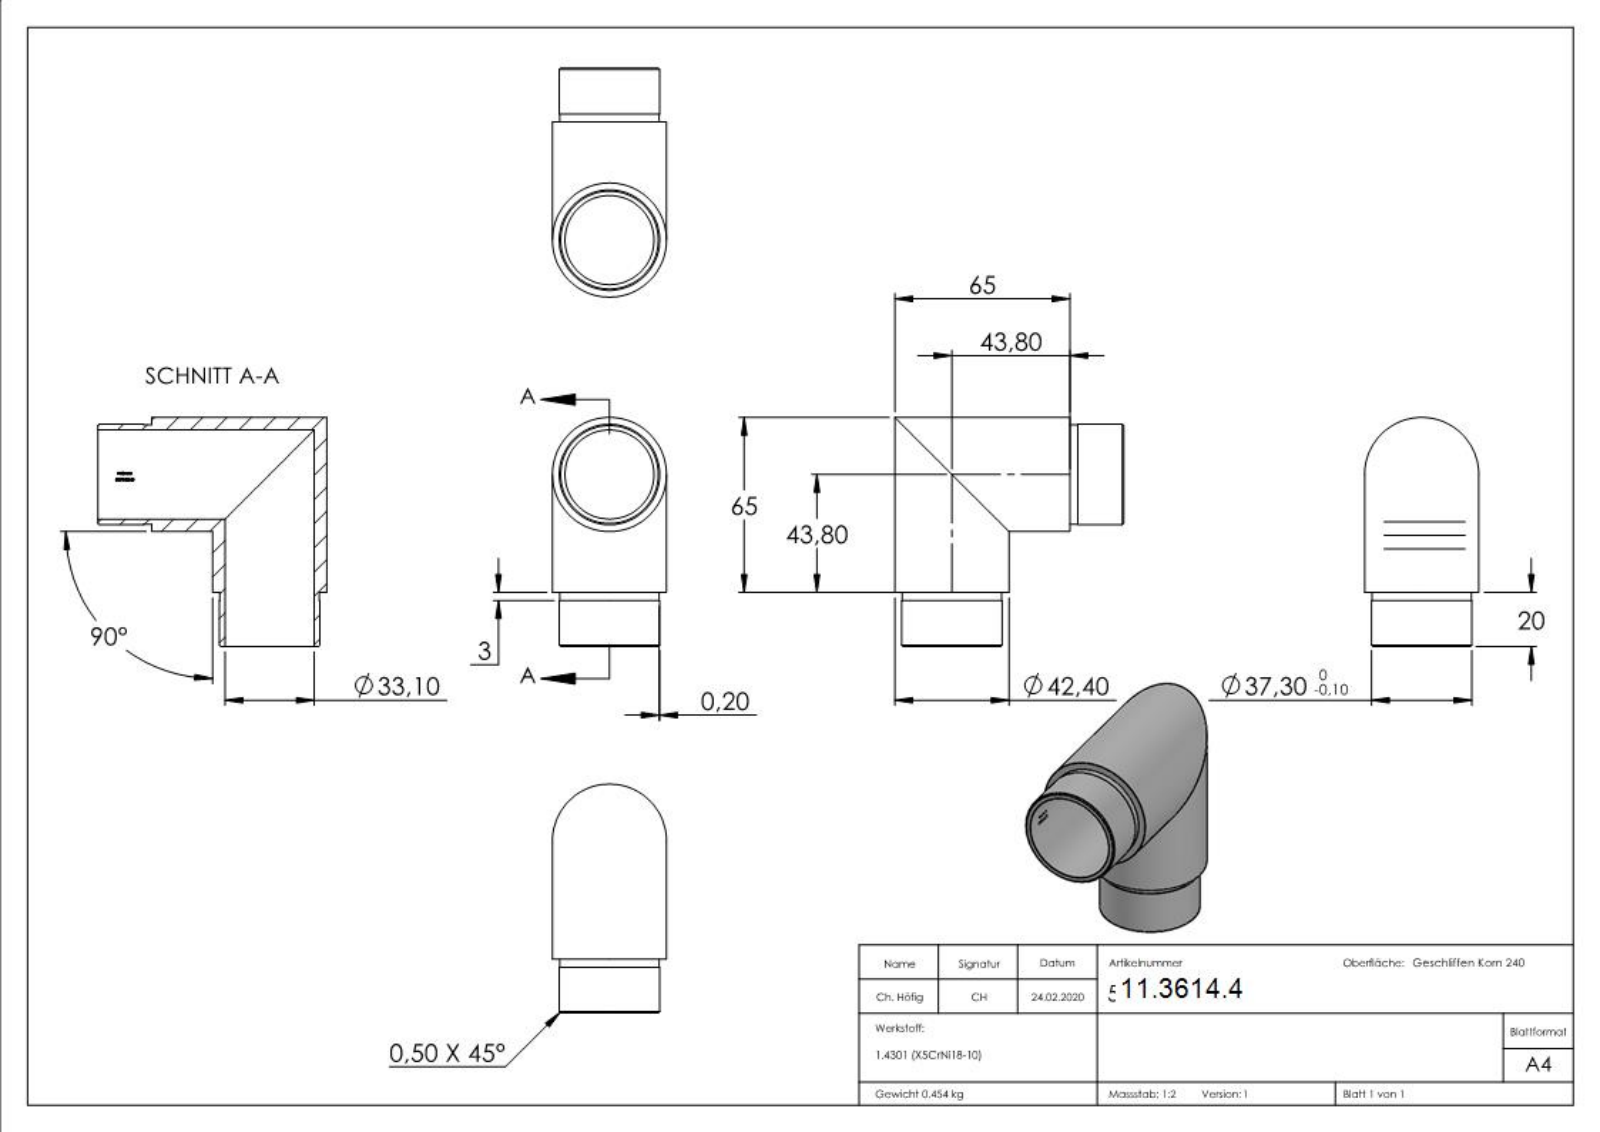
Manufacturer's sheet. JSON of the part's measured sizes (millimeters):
{"part_name": "56170-320-25", "step_written_by": "SolidWorks 2015 (CONFIG_CONTROL_DESIGN)", "units": "millimeters", "bodies": {"solids": 1, "faces": 263, "planar": 110, "cylindrical": 34, "other": 119}, "overall_size": [85, 85, 42.4], "volume_mm3": 57428, "surface_area_mm2": 30750, "round_holes": [[33.1, 2]], "round_bosses_or_shafts": [[42.4, 2], [37.3, 2], [36.9, 2]], "partial_cylinders_radius": [[16.65, 1]], "face_to_face_distances": [20, 17, 3, 0.79, 1.78, 0.71, 0.83, 2.77, 0.99, 2.45]}
